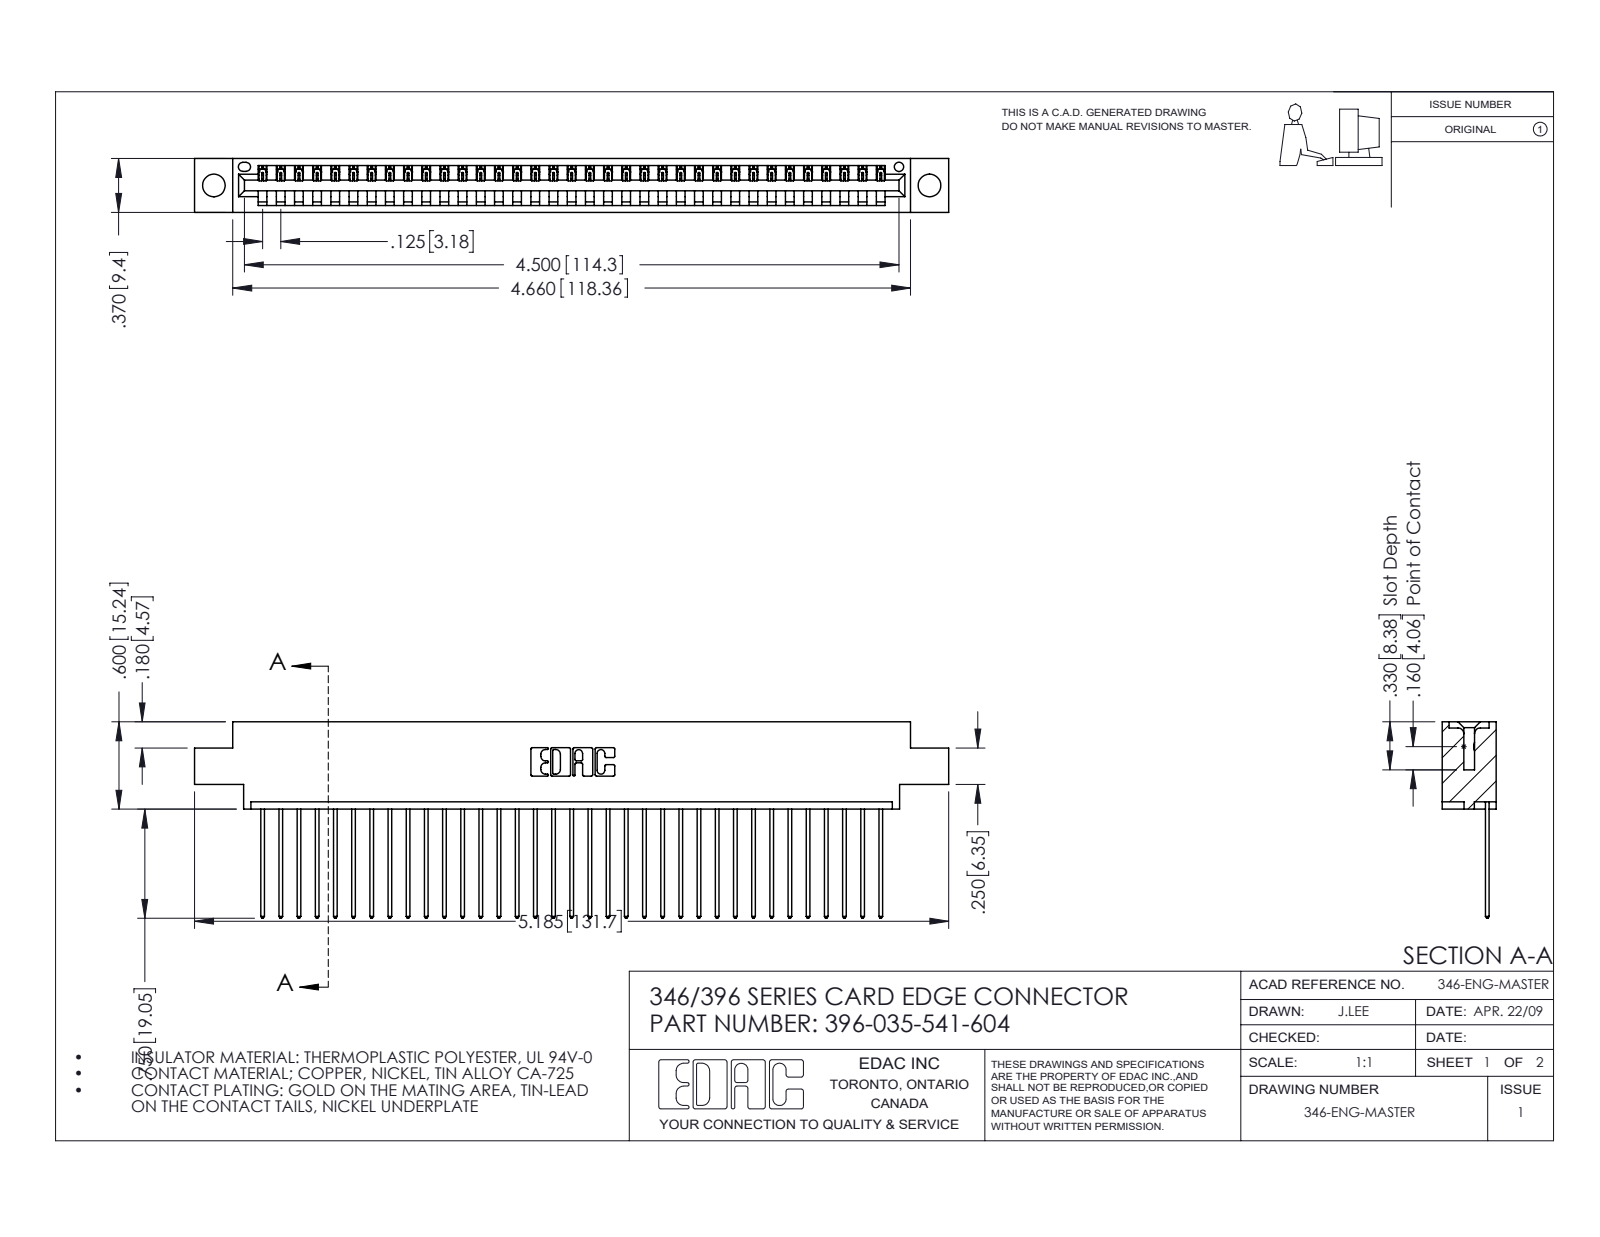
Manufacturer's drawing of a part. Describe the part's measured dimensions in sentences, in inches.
The part is named "345-292-001_345-293-141; 346 Part_0.170 Offset - 0.156 Dia-TH; 396-035-541-604". Its 3-D file was written by "SolidWorks 2016 (CONFIG_CONTROL_DESIGN)". It is 36 solids with 2156 faces: 1480 planar, 676 cylindrical and 0 other. Overall it measures 5.185 by 1.35 by 0.37 inches. Its volume is 0.759 cubic inches and its surface area 24.98 square inches. Round holes: 2 of diameter 0.156, 1 of diameter 0.064. Partial cylindrical surfaces (rounded edges, fillets, slot ends): 70 of radius 0.006, 70 of radius 0.01, 22 of radius 0.01, 6 of radius 0.007, 6 of radius 0.031, 3 of radius 0.026, 2 of radius 0.031, 2 of radius 0.04. The main face-to-face distances are 0.048, 0.322, 0.37, 0.25, 0.072, 0.298, 0.025, 0.148, 0.222, 0.1. The hole center spacings are 0.246, 4.711, 4.92.
